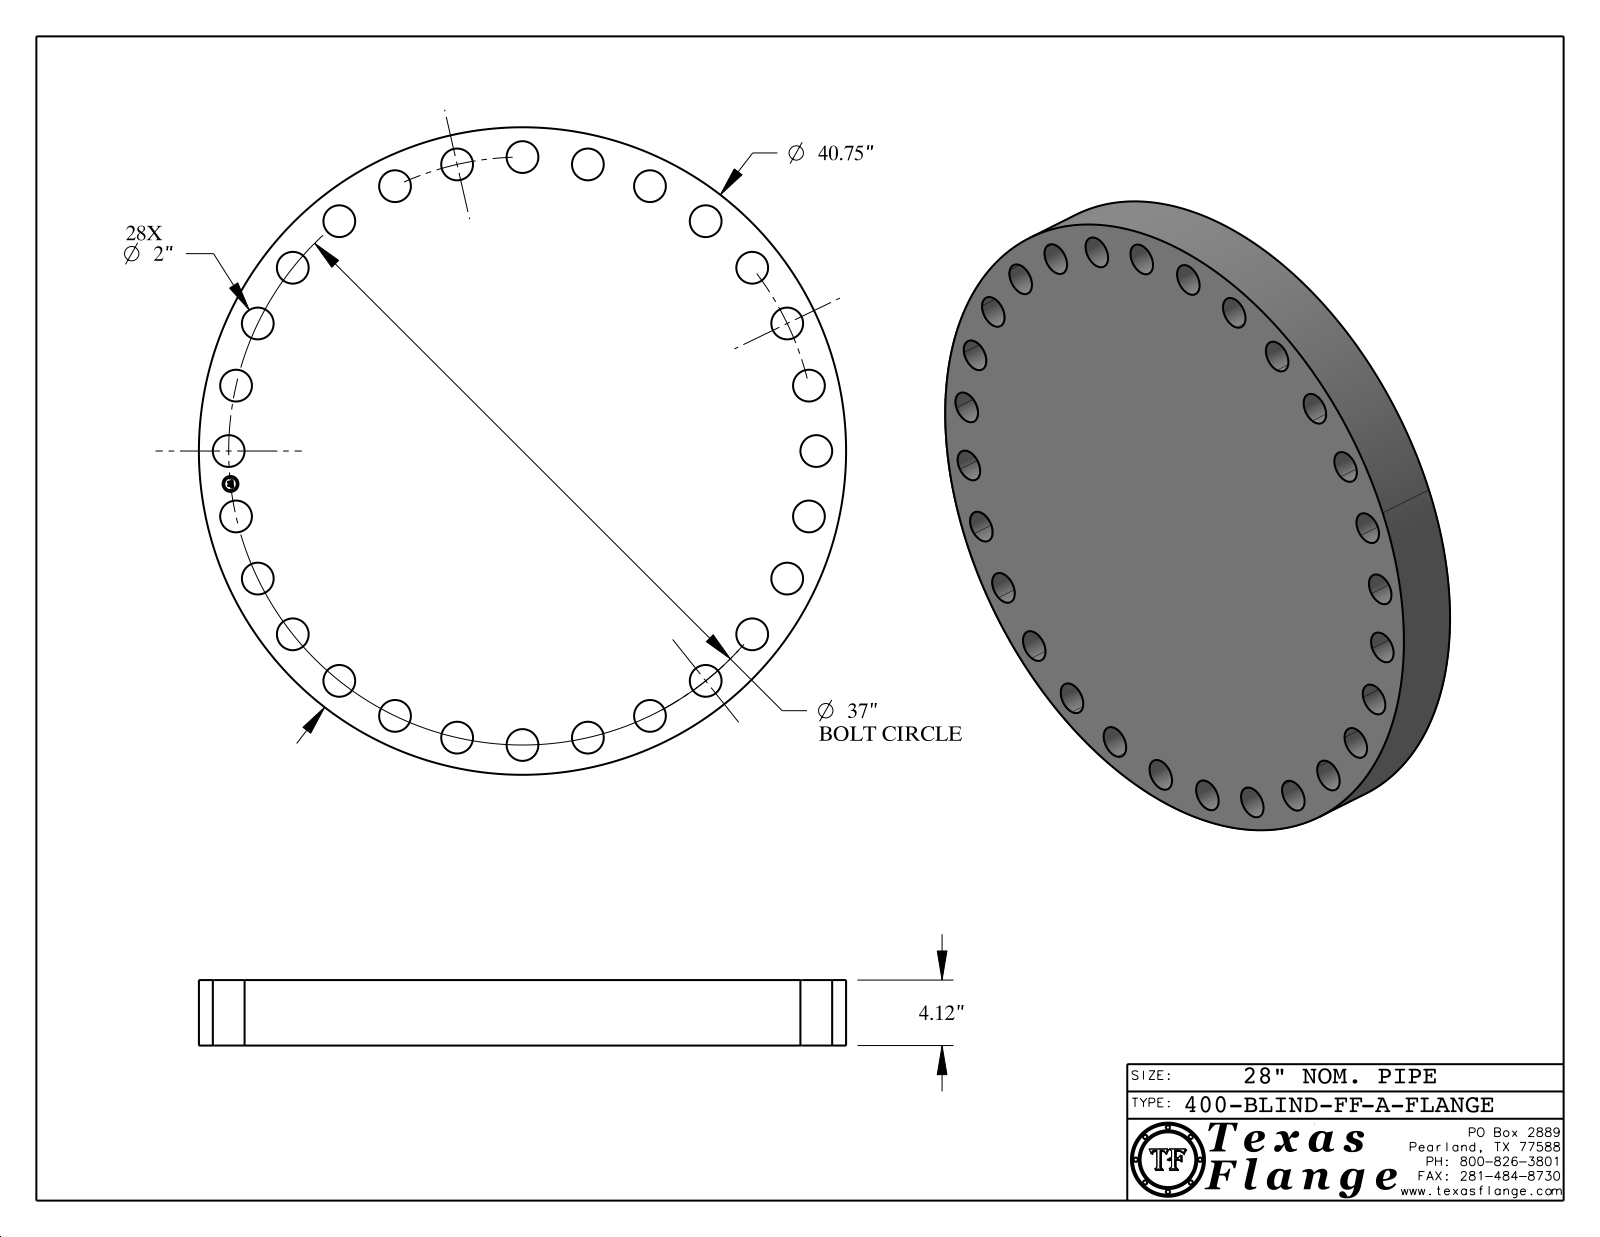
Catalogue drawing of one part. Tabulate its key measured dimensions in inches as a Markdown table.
| quantity | value |
| --- | --- |
| part name | 400-BLIND-FF, Series A |
| STEP written by | CATIA V5 STEP AP214 (AUTOMOTIVE_DESIGN) |
| units | inches |
| bodies | 1 solid, 445 faces (367 planar, 78 cylindrical, 0 other) |
| overall size | 40.75 × 40.75 × 4.12 |
| volume | 5 011 in³ |
| surface area | 3 685 in² |
| round holes (diameter × count) | 2 × 28, 1 × 1 |
| round bosses / shafts (diameter × count) | 0.061 × 8, 40.75 × 1, 0.788 × 1 |
| main face-to-face distances | 4.12, 0.015, 4.105, 0.298, 0.292, 0.054, 0.193, 0.248, 0.044, 0.15 |
| hole center spacings | 26.163, 31.329, 36.072, 36.767, 33.336, 4.143, 16.054, 23.069 |
